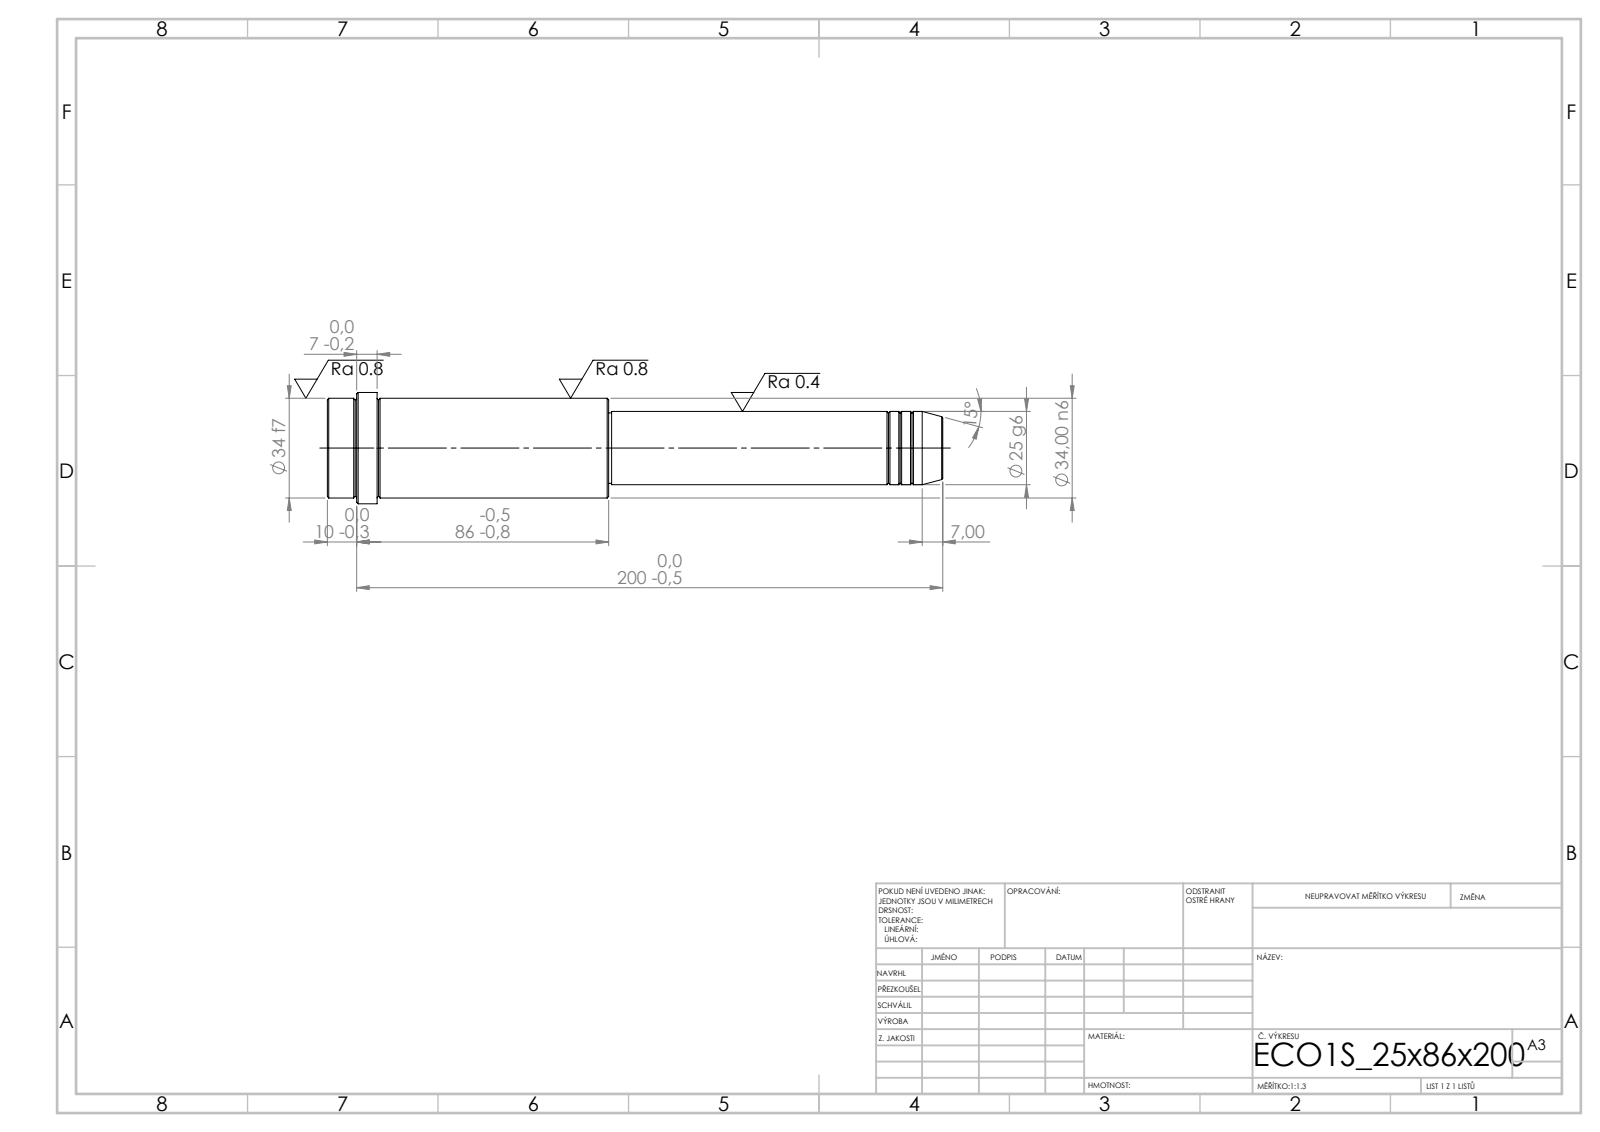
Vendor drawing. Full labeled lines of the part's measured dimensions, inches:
STEP written by: SolidWorks 2019 (CONFIG_CONTROL_DESIGN)
Units: inches
Bodies: 1 solid, 52 faces (6 planar, 16 cylindrical, 30 other)
Overall size (bounding box): 8.268 × 1.496 × 1.496
Volume: 8.785 in³ · Surface area: 33.5 in²
Round bosses / shafts (diameter × count): ⌀1.496 ×1, ⌀1.339 ×1, ⌀0.984 ×1, ⌀0.945 ×1
Main face-to-face distances: 3.78, 4.488, 8.268, 7.598, 3.11, 0.669, 7.874, 3.386, 0.276, 0.394
